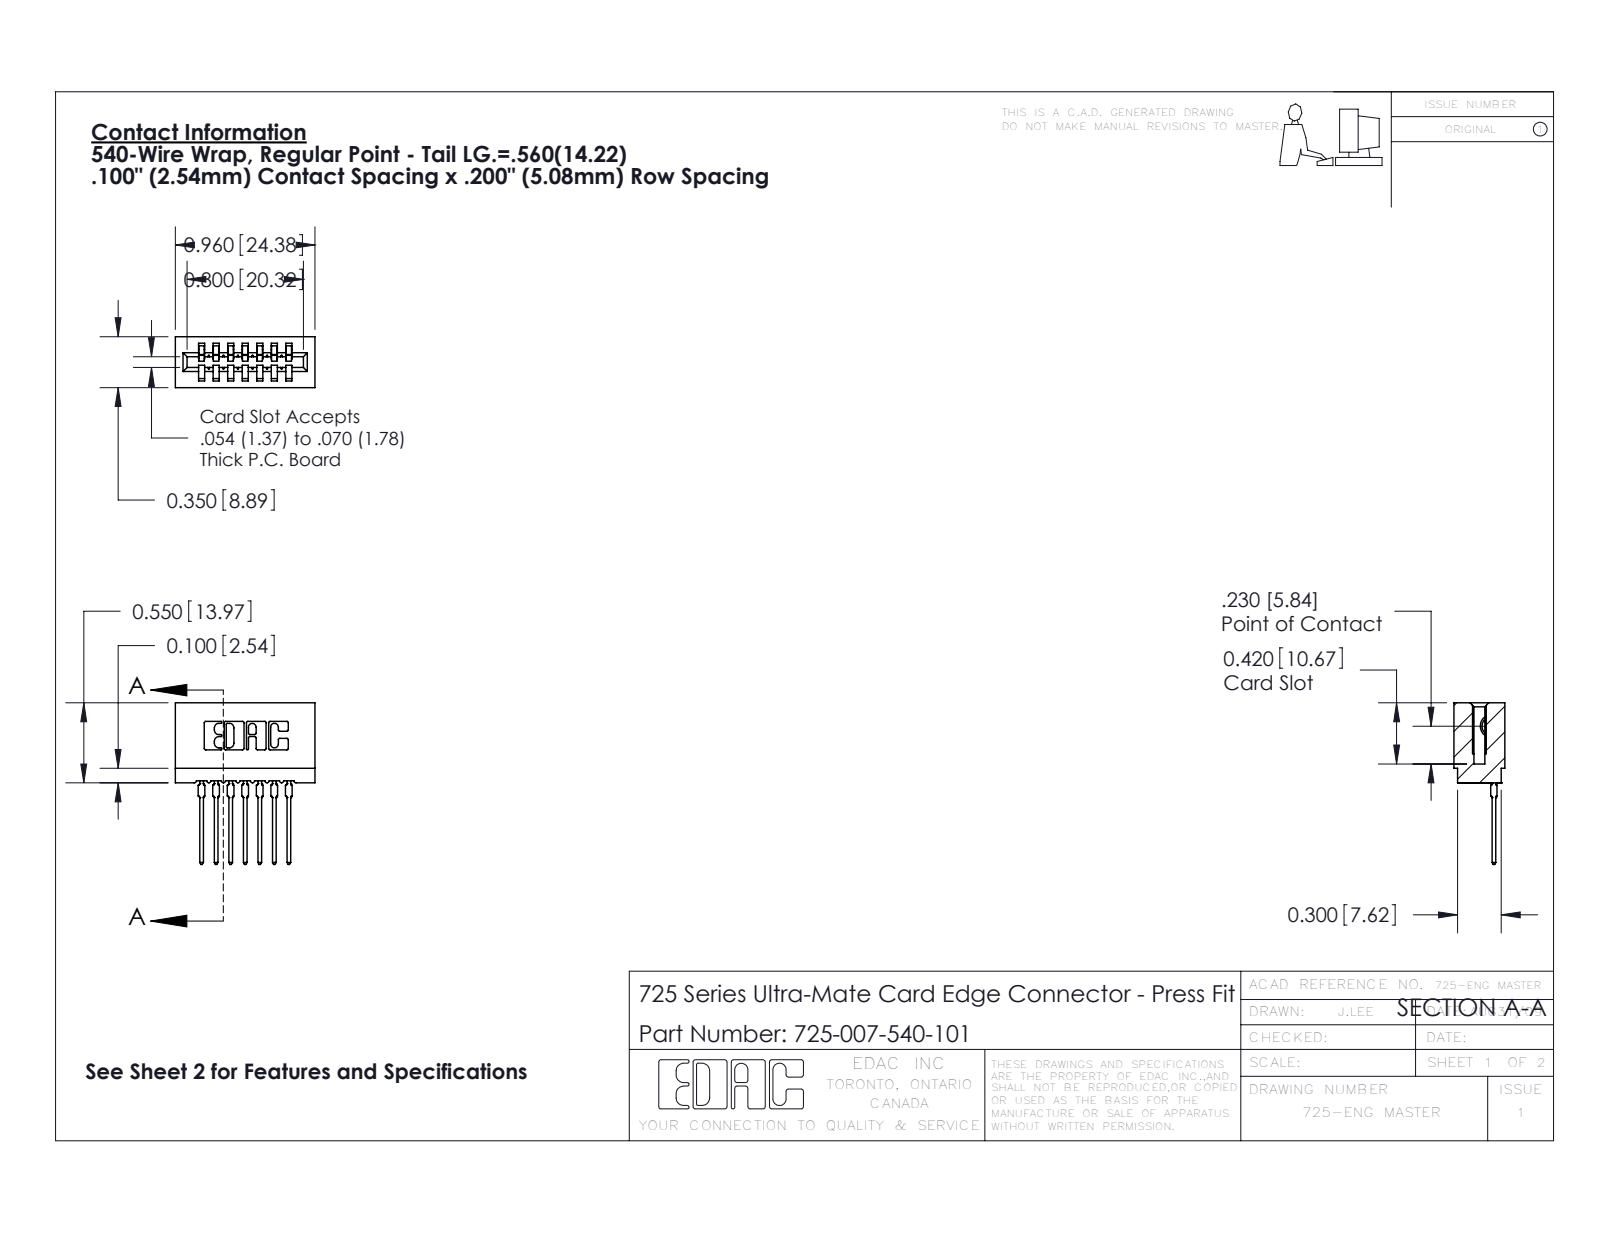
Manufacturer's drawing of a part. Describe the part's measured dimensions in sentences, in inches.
The part is named "745-292-001_540; 725 Part_Insulator Option - 01; 725-007-540-101". Its 3-D file was written by "SolidWorks 2016 (CONFIG_CONTROL_DESIGN)". It is 8 solids with 879 faces: 524 planar, 173 cylindrical and 182 other. Overall it measures 1.11 by 0.96 by 0.35 inches. Its volume is 0.126 cubic inches and its surface area 5.288 square inches. Partial cylindrical surfaces (rounded edges, fillets, slot ends): 22 of radius 0.01, 14 of radius 0.015, 14 of radius 0.021, 6 of radius 0.007, 6 of radius 0.031, 4 of radius 0.005, 4 of radius 0.011, 3 of radius 0.026. The main face-to-face distances are 0.1, 0.2, 0.3, 0.042, 0.4, 0.142, 0.058, 0.242, 0.158, 0.5.
